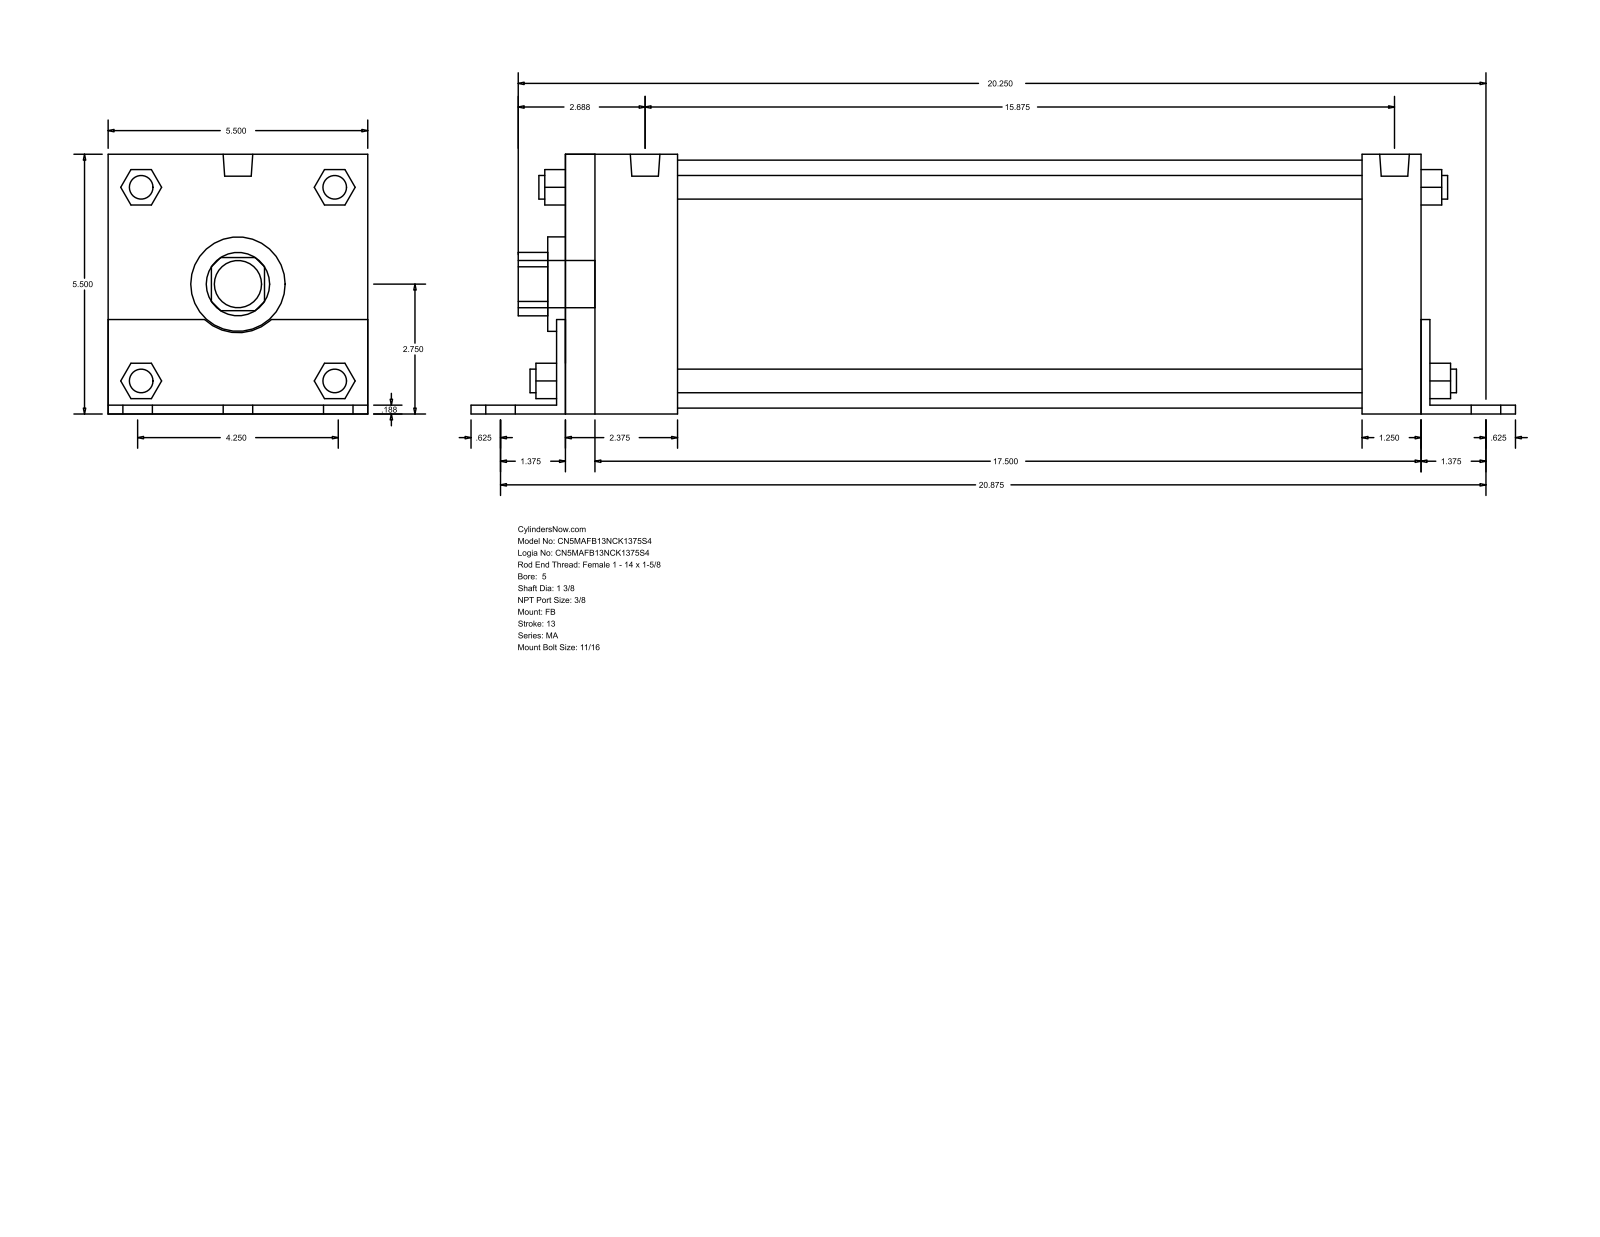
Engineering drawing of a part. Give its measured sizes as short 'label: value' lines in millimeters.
name: MA_FB__0500_1.375
written by: GSSL Pune (CONFIG_CONTROL_DESIGN)
unit: mm
bodies: 0 solids, 140 faces (105 planar, 35 cylindrical, 0 other)
size: 561.98 × 139.75 × 139.7
holes: 1× ⌀34.92, 1× ⌀50.8, 1× ⌀133.35
bosses: 6× ⌀17.46, 4× ⌀12.7, 4× ⌀11.11, 2× ⌀15.93, 1× ⌀25.4
rounds: 1× R17.06, 1× R26.16
face distances: 139.7, 4.76, 139.75, 4.71, 134.99, 460.37, 4.77, 465.14, 465.13, 469.9
